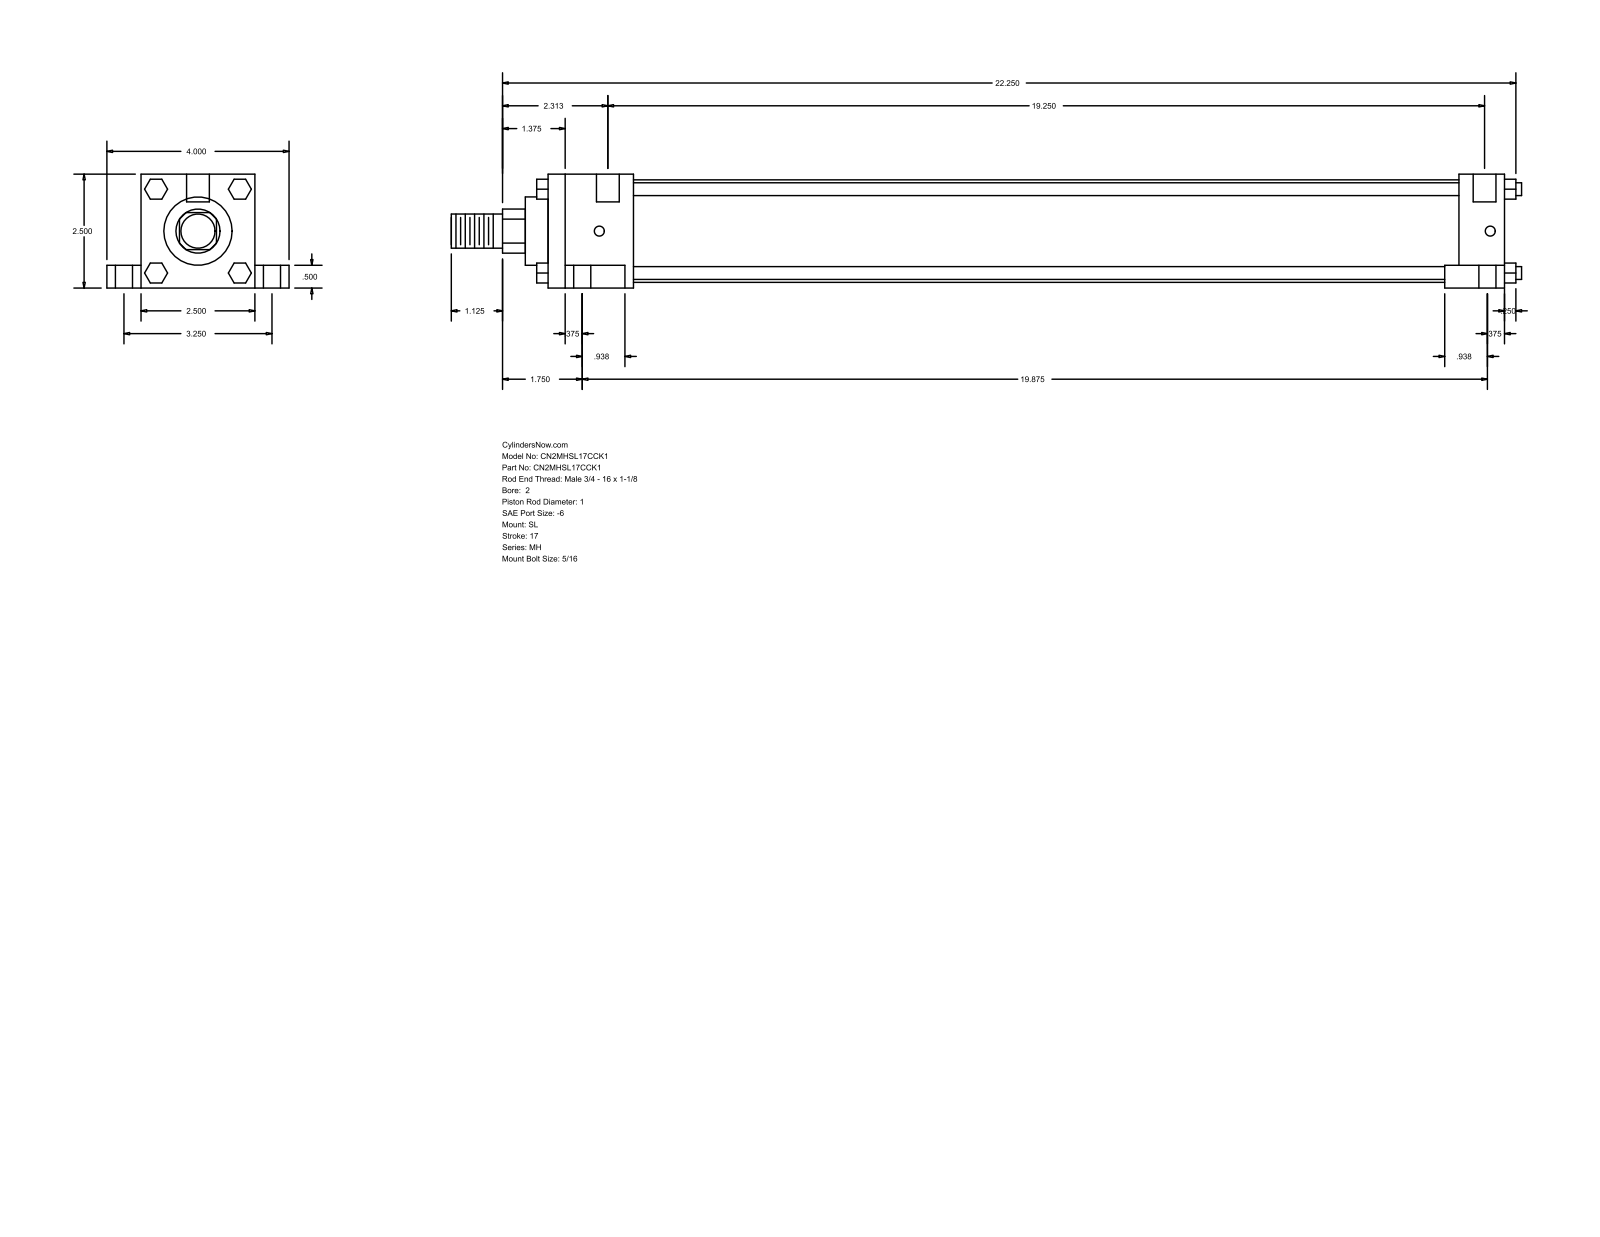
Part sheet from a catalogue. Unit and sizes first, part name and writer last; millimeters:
Units: millimetres
Overall size (bounding box): 596.9 × 101.6 × 63.5
Round holes (diameter × count): ⌀5.56 ×4, ⌀9.53 ×4, ⌀15.88 ×4, ⌀12.7 ×2
Round bosses / shafts (diameter × count): ⌀7.14 ×4, ⌀57.15 ×1, ⌀38.1 ×1, ⌀25.4 ×1, ⌀19.05 ×1
Partial cylindrical surfaces — rounded edges, fillets, slot ends (radius × count): R12.29 ×1
Main face-to-face distances: 63.5, 533.4, 12.7, 19.05, 50.8, 82.55, 25.4, 508, 47.63, 460.37
Hole centre spacings: 41.3, 42.36, 43.67, 82.54, 492.26, 496.88, 497.01, 504.82
Bodies: 0 solids, 148 faces (112 planar, 36 cylindrical, 0 other)
Part name (STEP PRODUCT): MH_SL__0200_1
STEP written by: GSSL Pune (CONFIG_CONTROL_DESIGN)
